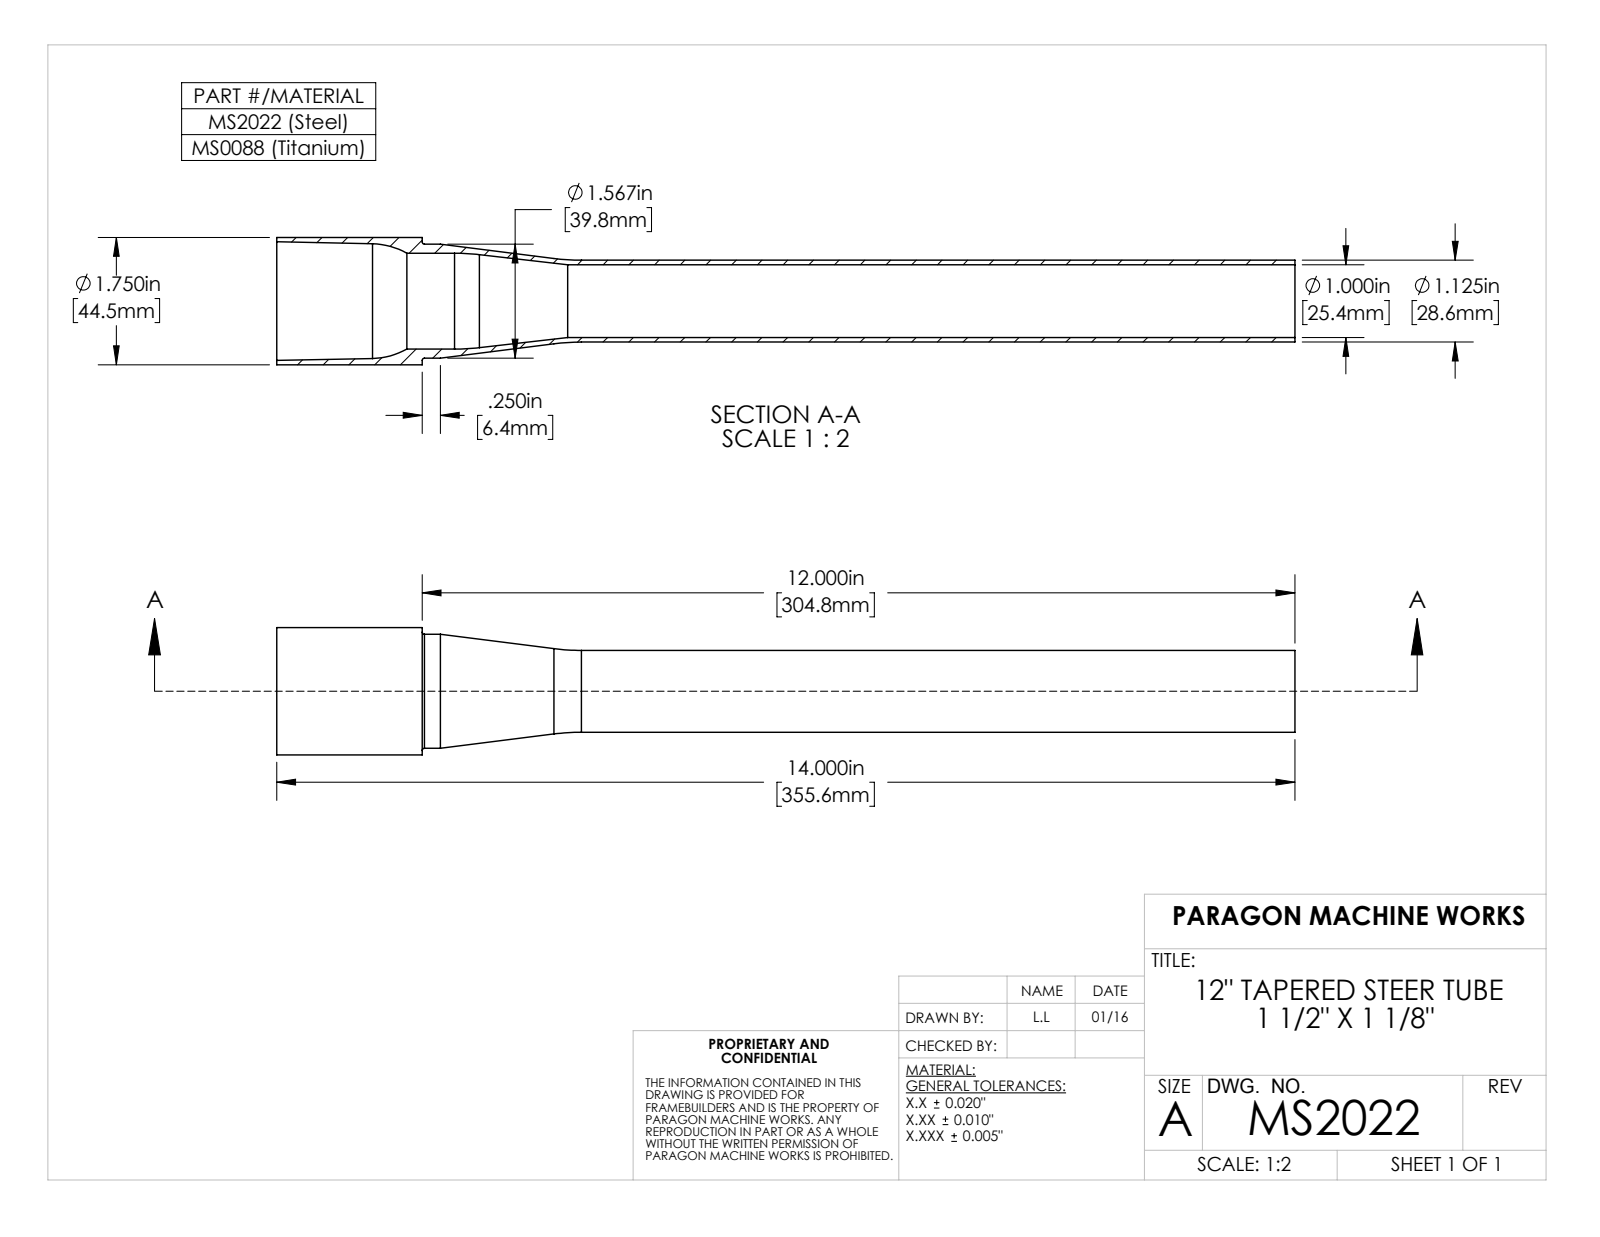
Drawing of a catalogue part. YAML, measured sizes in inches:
part_name: "MS2022"
step_written_by: "SolidWorks 2016 (AUTOMOTIVE_DESIGN)"
units: inches
bodies: {solids: 1, faces: 27, planar: 3, cylindrical: 10, other: 14}
overall_size: [14, 1.75, 1.75]
volume: 3.821
surface_area: 104.8
round_holes:
  - {diameter: 1, count: 1}
  - {diameter: 1.317, count: 1}
round_bosses_or_shafts:
  - {diameter: 1.75, count: 1}
  - {diameter: 1.567, count: 1}
  - {diameter: 1.125, count: 1}
face_to_face_distances: [2, 14, 12]
